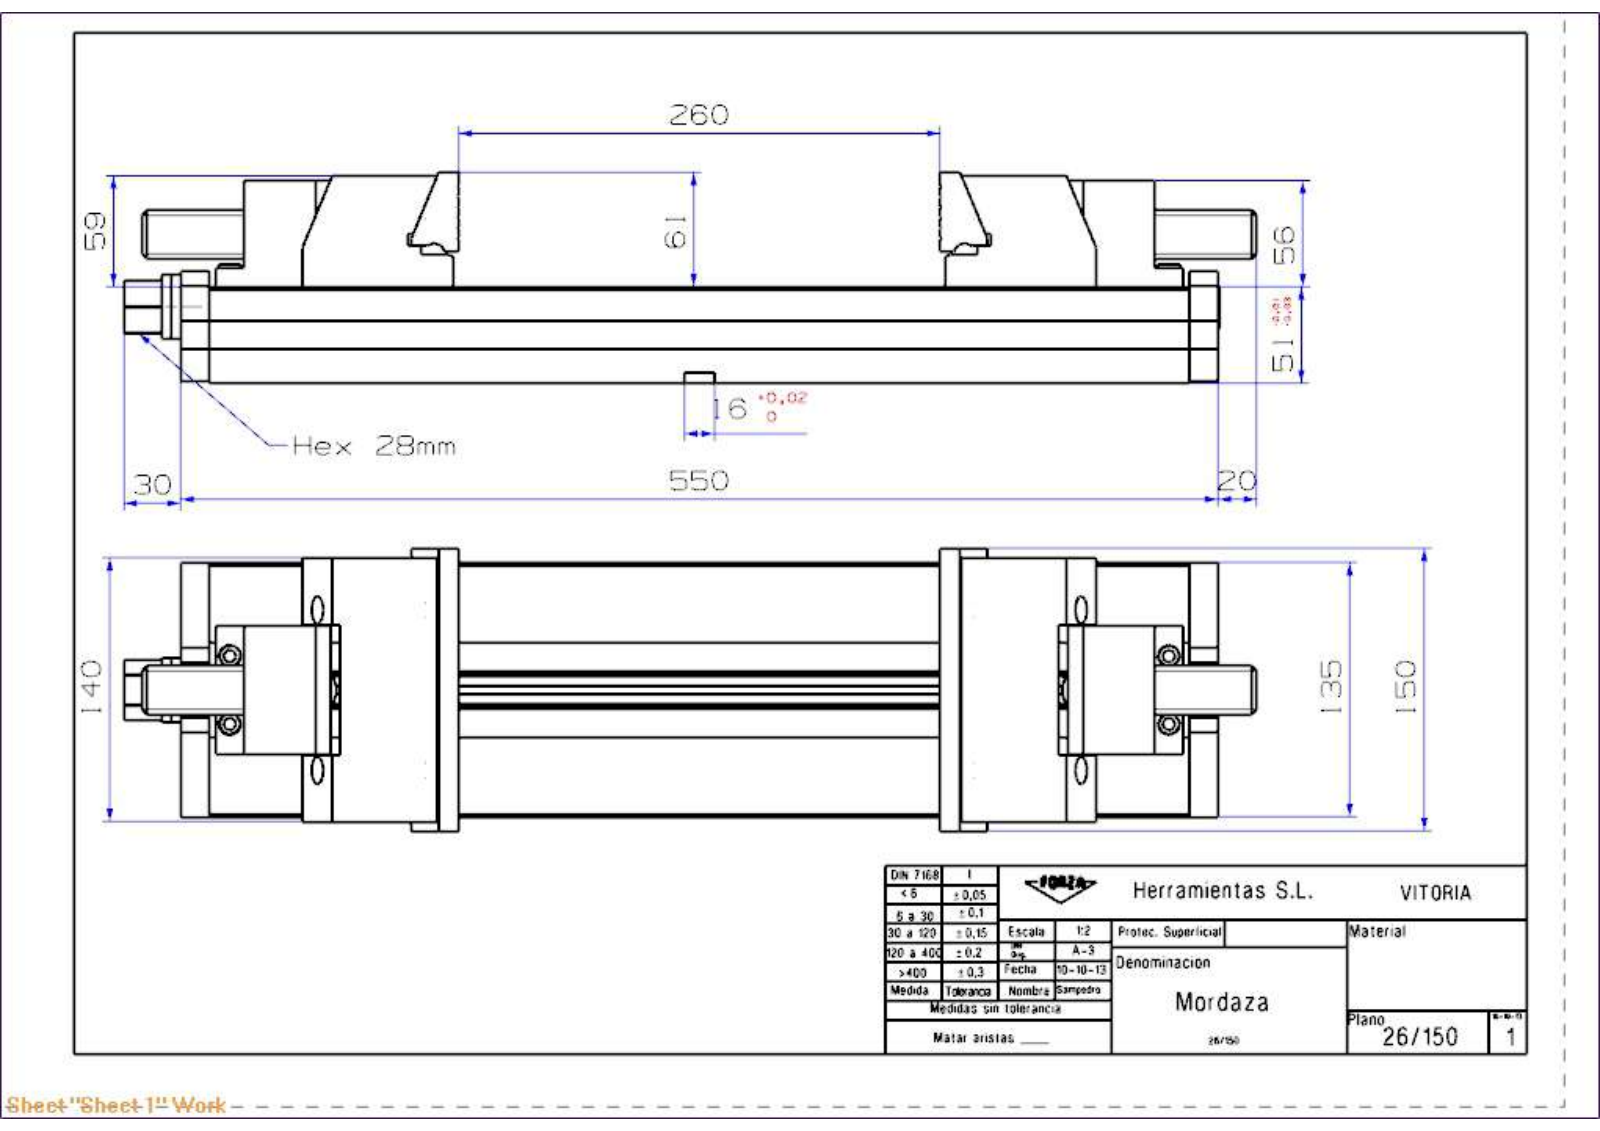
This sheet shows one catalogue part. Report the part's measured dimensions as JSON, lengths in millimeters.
{"part_name": "26_150_Mordaza", "step_written_by": "SIEMENS PLM Software NX 7.5 (CONFIG_CONTROL_DESIGN)", "units": "millimeters", "bodies": {"solids": 65, "faces": 1662, "planar": 938, "cylindrical": 385, "other": 339}, "overall_size": [600.4, 150, 111.8], "volume_mm3": 4492000, "surface_area_mm2": 760257, "round_holes": [[10, 14], [5, 12], [8.5, 11], [6.99, 10], [4.35, 8], [9, 8], [14, 8], [8.78, 5], [30, 5], [10.58, 4], [12, 4], [10.5, 3]], "round_bosses_or_shafts": [[47, 4], [11.7, 4], [10, 4], [51, 2], [45, 2], [30, 2], [27.7, 2], [26, 2]], "partial_cylinders_radius": [[8, 5], [0.5, 4], [10, 3], [5, 2], [6, 2], [17.25, 2], [18, 2], [2, 1]], "face_to_face_distances": [51, 17.3, 33.7, 2.5, 15.7, 13, 71.5, 129.5, 31, 32.5], "hole_center_spacings": [40, 62.7, 50, 29.25, 36, 37.75, 53.81, 67]}
